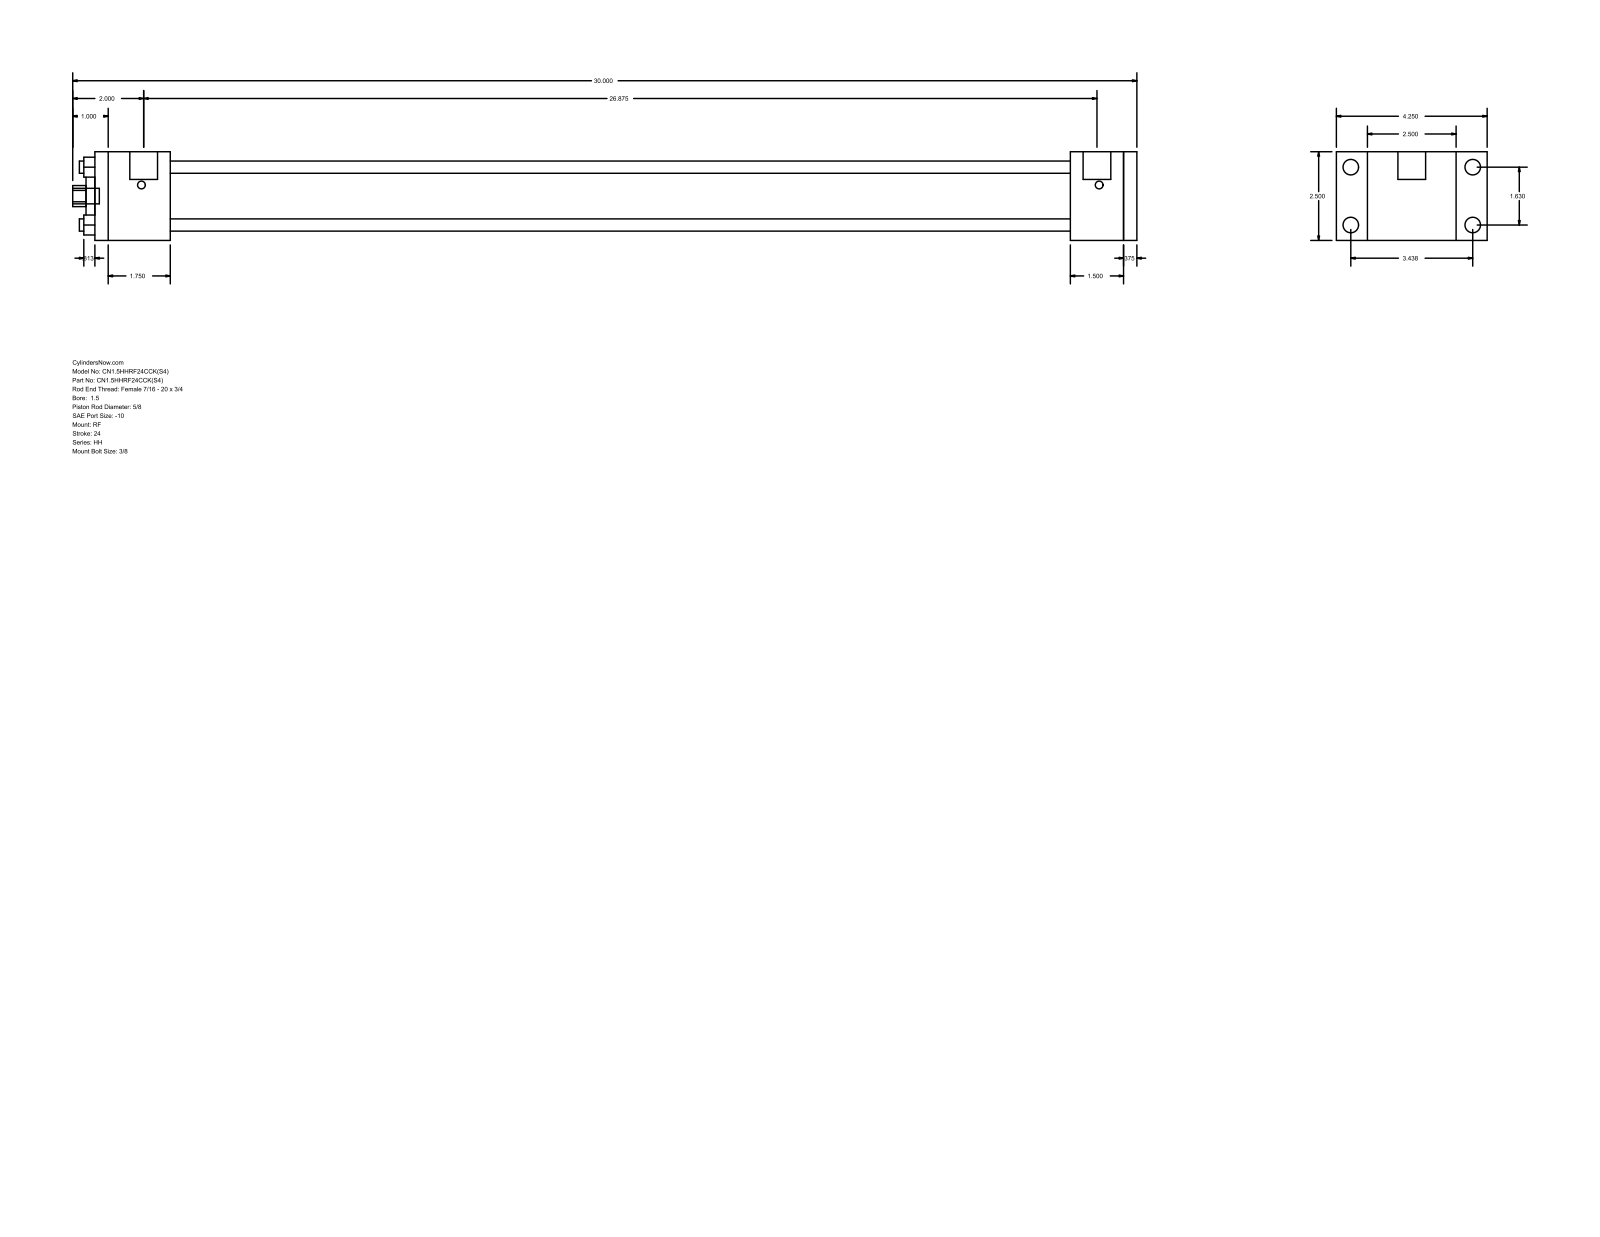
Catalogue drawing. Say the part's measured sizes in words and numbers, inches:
The part is named "HH_RF__0150_0.625". Its 3-D file was written by "GSSL Pune (CONFIG_CONTROL_DESIGN)". It is 0 solids with 92 faces: 64 planar, 28 cylindrical and 0 other. Overall it measures 30 by 4.25 by 2.5 inches. Round holes: 4 of diameter 0.345, 1 of diameter 0.625, 1 of diameter 1.125, 1 of diameter 1.75. Round bosses or shafts: 4 of diameter 0.438, 4 of diameter 0.219, 2 of diameter 0.781, 1 of diameter 0.437. Partial cylindrical surfaces (rounded edges, fillets, slot ends): 1 of radius 0.297. The main face-to-face distances are 2.5, 29.375, 0.375, 1.5, 29, 2.125, 27.5, 25.375, 26.875, 27.25. The hole center spacings are 1.152, 1.63, 2.305.
